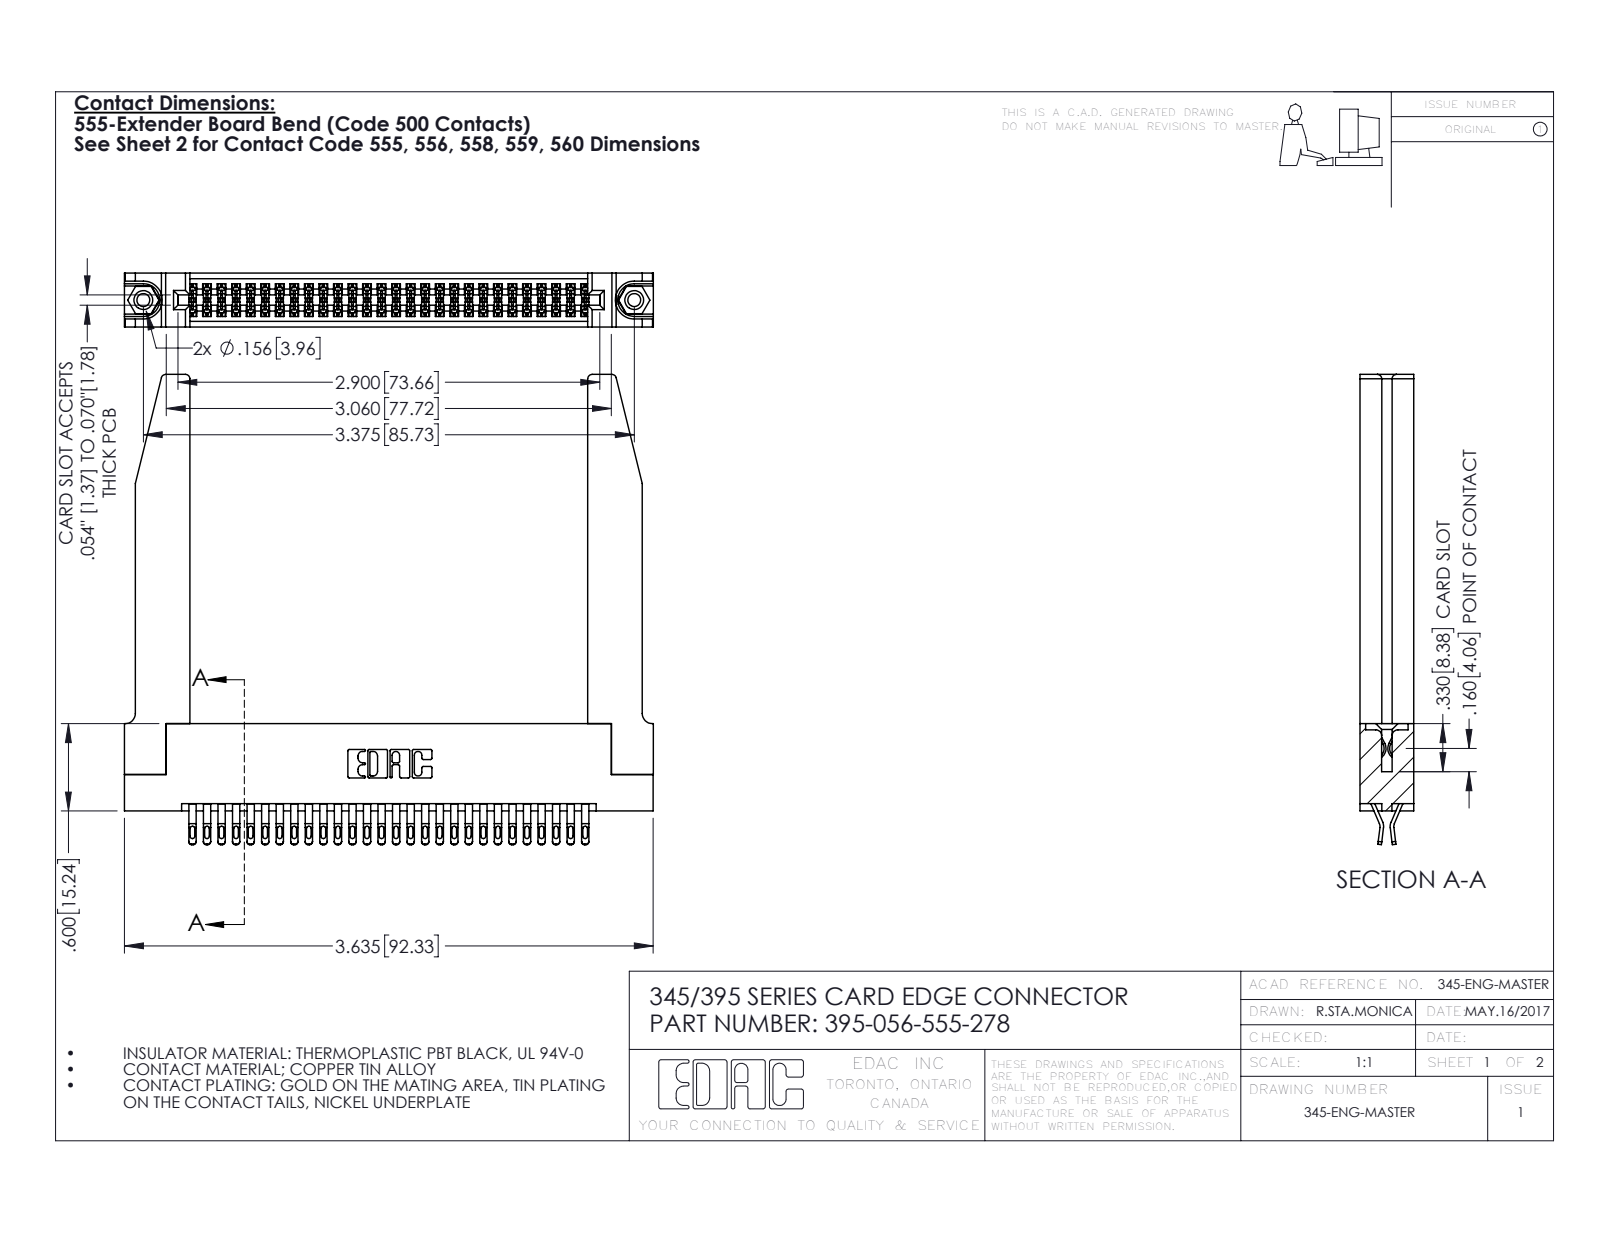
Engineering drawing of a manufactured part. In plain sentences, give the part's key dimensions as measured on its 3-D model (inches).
The part is named "345 Part_Flush Mounting Lugs - 0.156 Dia-TH; 345-292-001_555 Tail; 345-250-001_345-250-001-102; 345-220-078_345-220-078 (+1 more)". Its 3-D file was written by "SolidWorks 2016 (CONFIG_CONTROL_DESIGN)". It is 61 solids with 3496 faces: 1958 planar, 1486 cylindrical and 52 other. Overall it measures 3.636 by 3.232 by 0.37 inches. Its volume is 1.024 cubic inches and its surface area 31.68 square inches. Round holes: 2 of diameter 0.089, 2 of diameter 0.125, 2 of diameter 0.156, 1 of diameter 0.064. Round bosses or shafts: 2 of diameter 0.155. Partial cylindrical surfaces (rounded edges, fillets, slot ends): 140 of radius 0.016, 112 of radius 0.02, 84 of radius 0.006, 22 of radius 0.01, 8 of radius 0.03, 6 of radius 0.007, 6 of radius 0.031, 3 of radius 0.026. The main face-to-face distances are 0.37, 0.072, 0.298, 0.2, 0.025, 0.098, 0.272, 0.225, 0.148, 0.15. The hole center spacings are 0.27, 3.14, 3.375.
